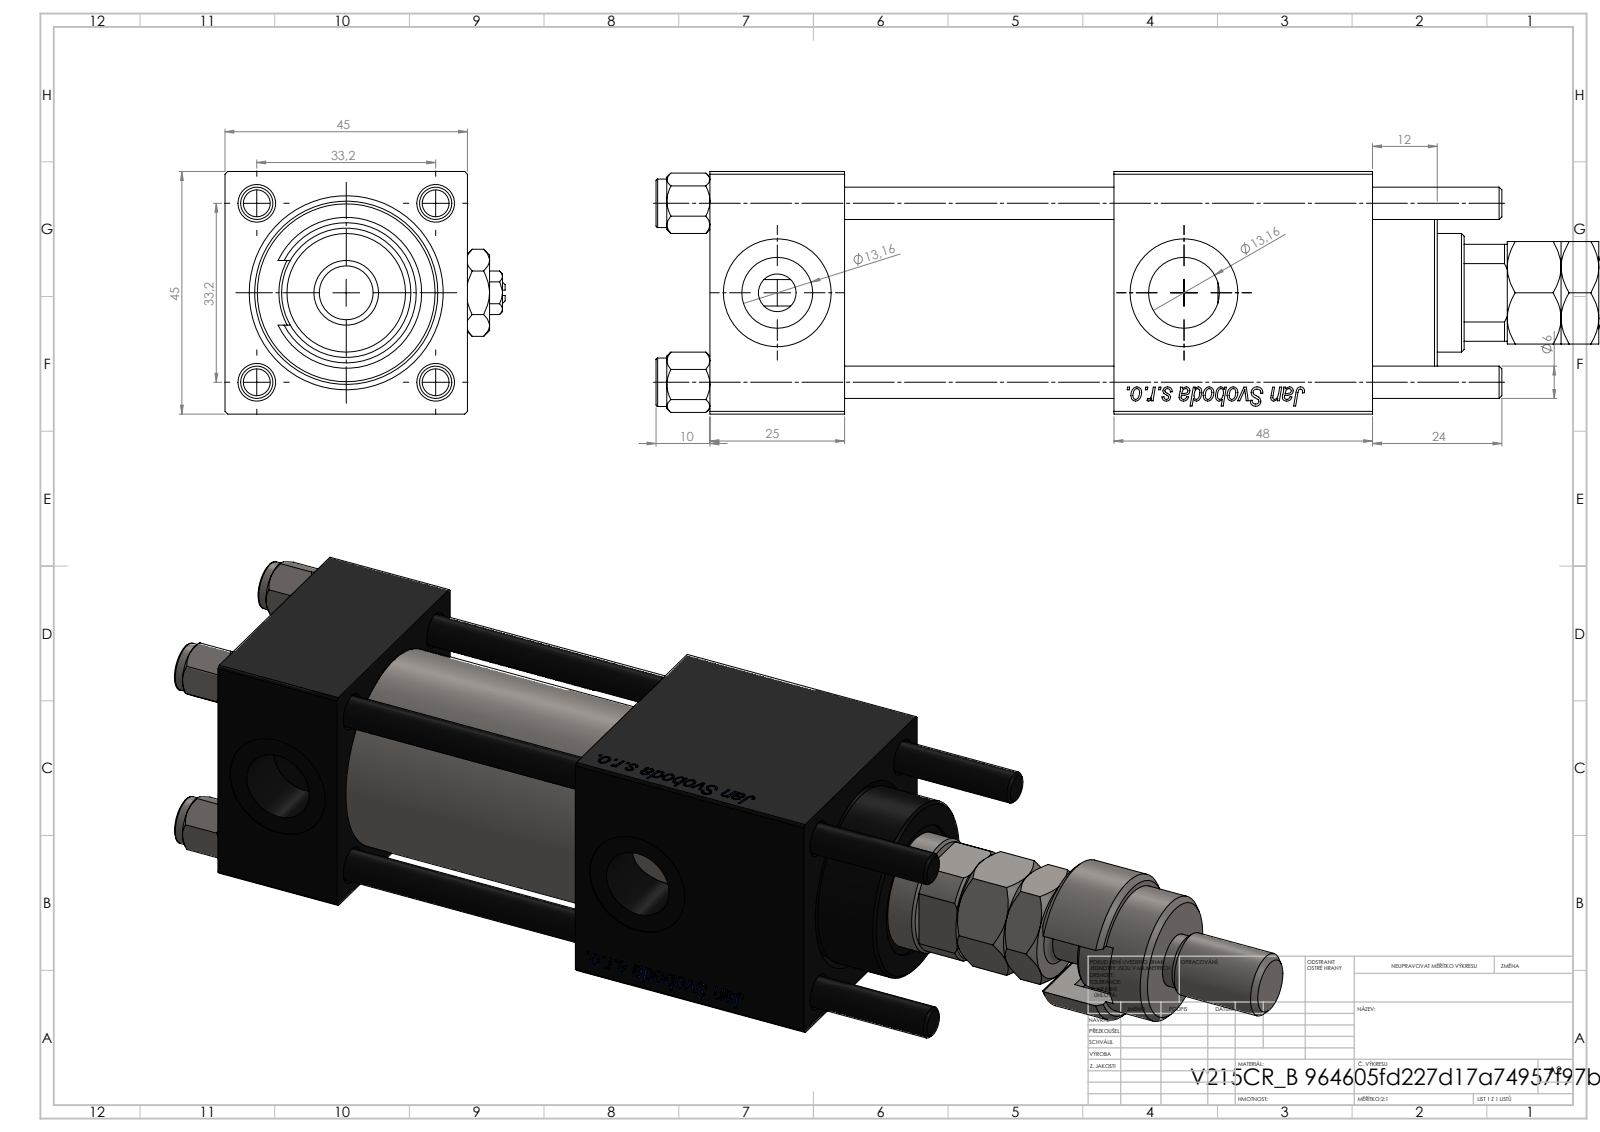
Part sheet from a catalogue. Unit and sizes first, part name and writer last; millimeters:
Units: millimetres
Overall size (bounding box): 219 × 52 × 45
Round holes (diameter × count): ⌀6 ×4, ⌀7 ×2, ⌀13.16 ×2, ⌀20 ×2, ⌀10.5 ×1, ⌀22 ×1, ⌀24 ×1, ⌀25 ×1, ⌀32 ×1, ⌀33 ×1
Round bosses / shafts (diameter × count): ⌀9 ×4, ⌀38 ×1, ⌀34 ×1, ⌀28 ×1, ⌀18 ×1, ⌀12 ×1, ⌀11 ×1, ⌀10 ×1
Partial cylindrical surfaces — rounded edges, fillets, slot ends (radius × count): R9.75 ×1, R10.5 ×1
Main face-to-face distances: 45, 25, 123, 50, 98, 75, 44.8, 48, 94.3, 69.3
Hole centre spacings: 23.48, 33.2, 46.95, 75.5
Volume: 230 661 mm³ · Surface area: 85 751 mm²
Bodies: 15 solids, 1341 faces (506 planar, 101 cylindrical, 734 other)
Part name (STEP PRODUCT): FEMALE_PART_FOR_DFA; NUT_M5_B; V215CR_VCP_B; Zatka_pro_OIL_PORT (+4 more)
STEP written by: SolidWorks 2019 (CONFIG_CONTROL_DESIGN)
